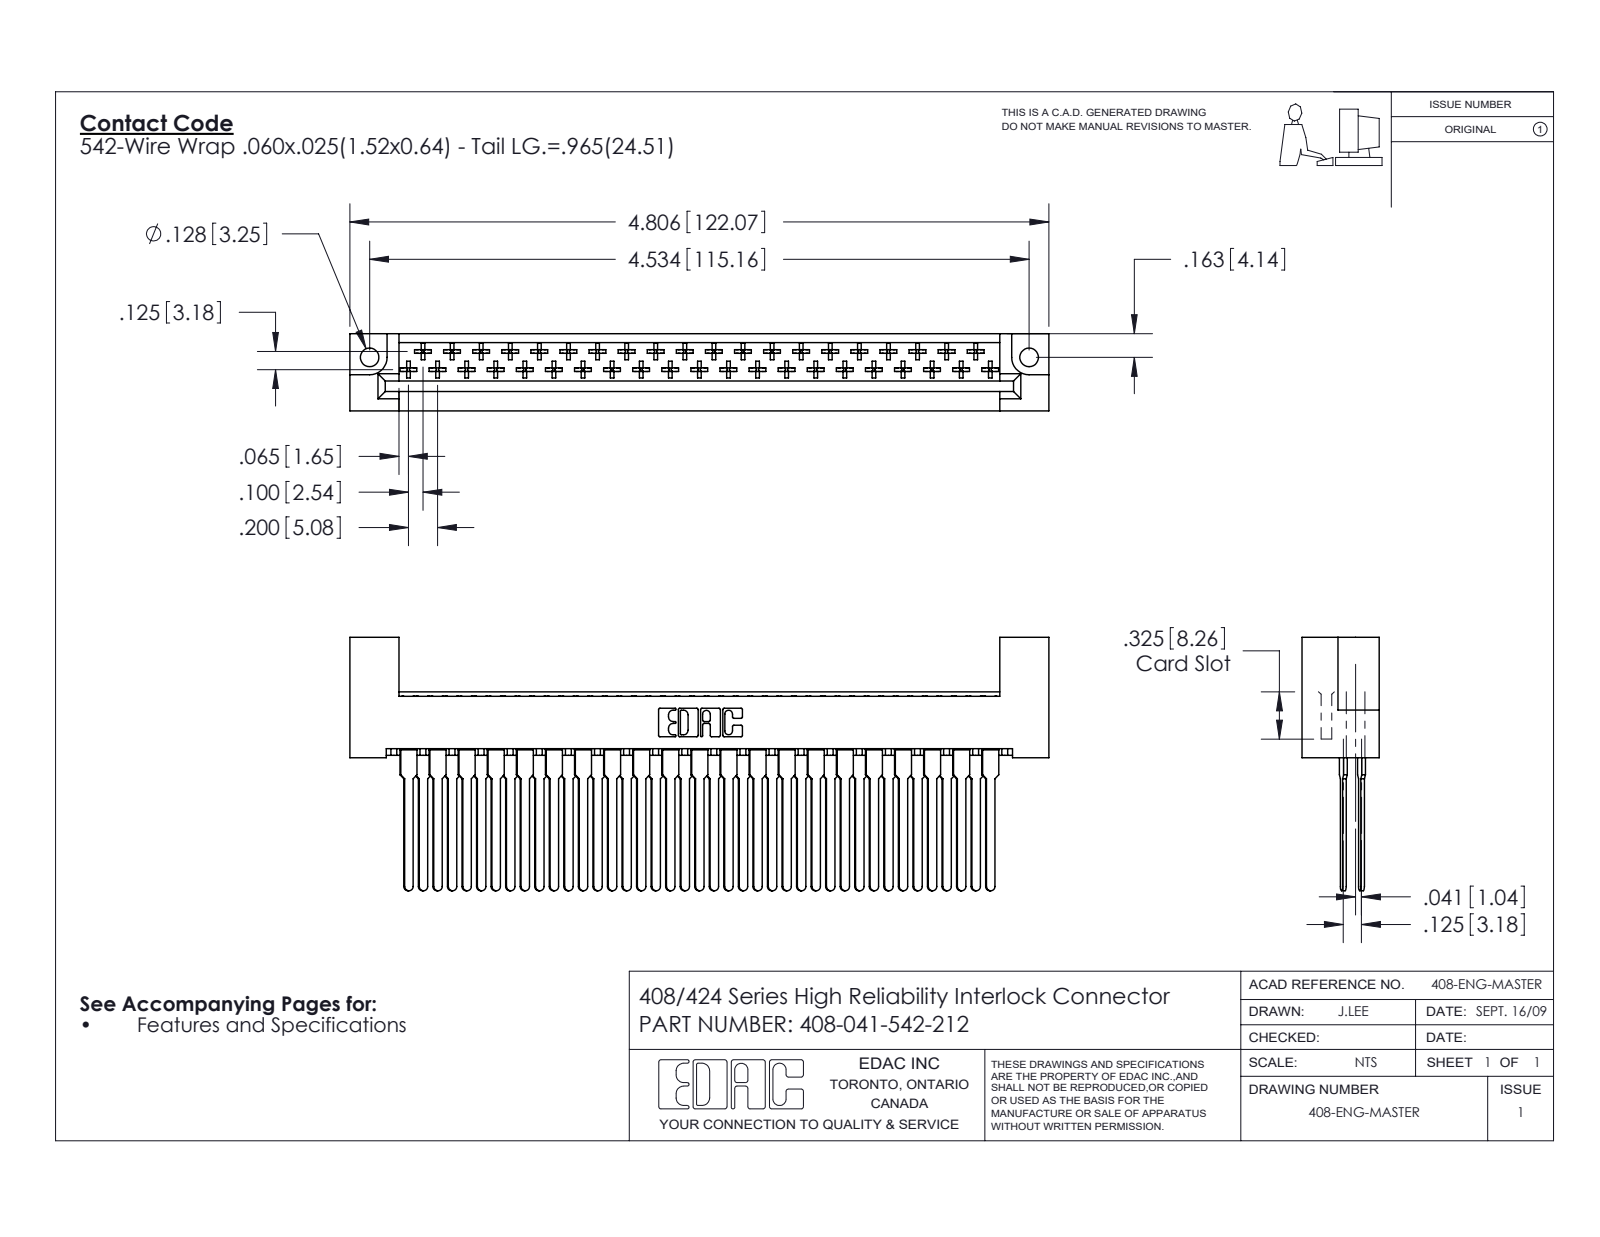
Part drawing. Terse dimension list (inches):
name: 408 Part_041 - 2; 408-290-001_408-290-142; 408-047-542-212
written by: SolidWorks 2016 (CONFIG_CONTROL_DESIGN)
unit: in
bodies: 42 solids, 2312 faces (1729 planar, 419 cylindrical, 164 other)
size: 4.806 × 1.742 × 0.531
volume: 0.974 in³; area: 33.25 in²
holes: 2× ⌀0.128
rounds: 246× R0.01, 43× R0.02, 41× R0.03, 22× R0.01, 6× R0.007, 6× R0.031, 3× R0.026, 2× R0.12
face distances: 0.531, 0.125, 0.1, 0.025, 0.025, 0.361, 0.235, 0.259, 0.217, 0.272
hole spacings: 4.534
